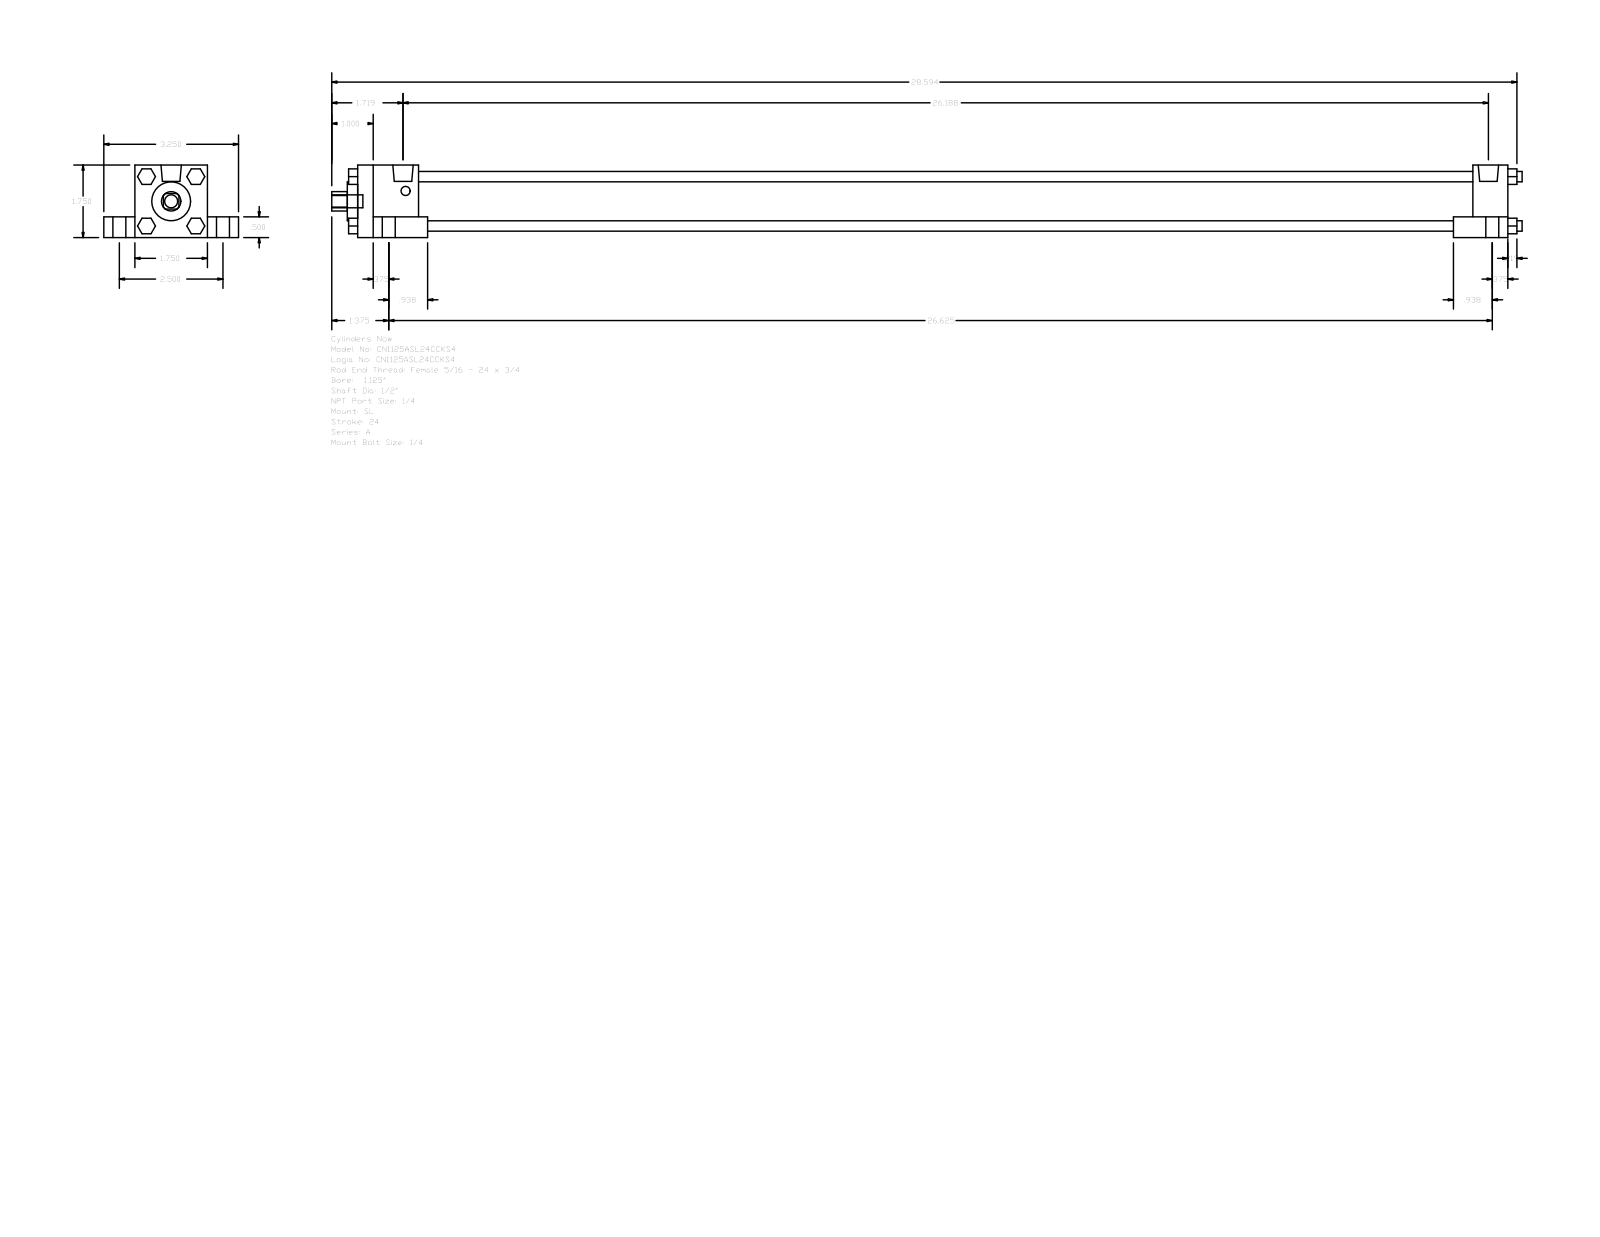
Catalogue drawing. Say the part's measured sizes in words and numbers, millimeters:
The part is named "A_SL__0112_0.5". Its 3-D file was written by "GSSL Pune (CONFIG_CONTROL_DESIGN)". It is 0 solids with 150 faces: 114 planar, 36 cylindrical and 0 other. Overall it measures 729.46 by 82.55 by 44.45 millimeters. Round holes: 1 of diameter 12.7, 1 of diameter 23.81, 1 of diameter 31.88. Round bosses or shafts: 5 of diameter 7.94, 4 of diameter 14.29, 4 of diameter 6.35, 4 of diameter 5.56, 2 of diameter 12.49. Partial cylindrical surfaces (rounded edges, fillets, slot ends): 1 of radius 5.94. The main face-to-face distances are 44.46, 31.76, 12.7, 19.04, 63.5, 704.85, 683.41, 21.44, 37.3, 646.11.
